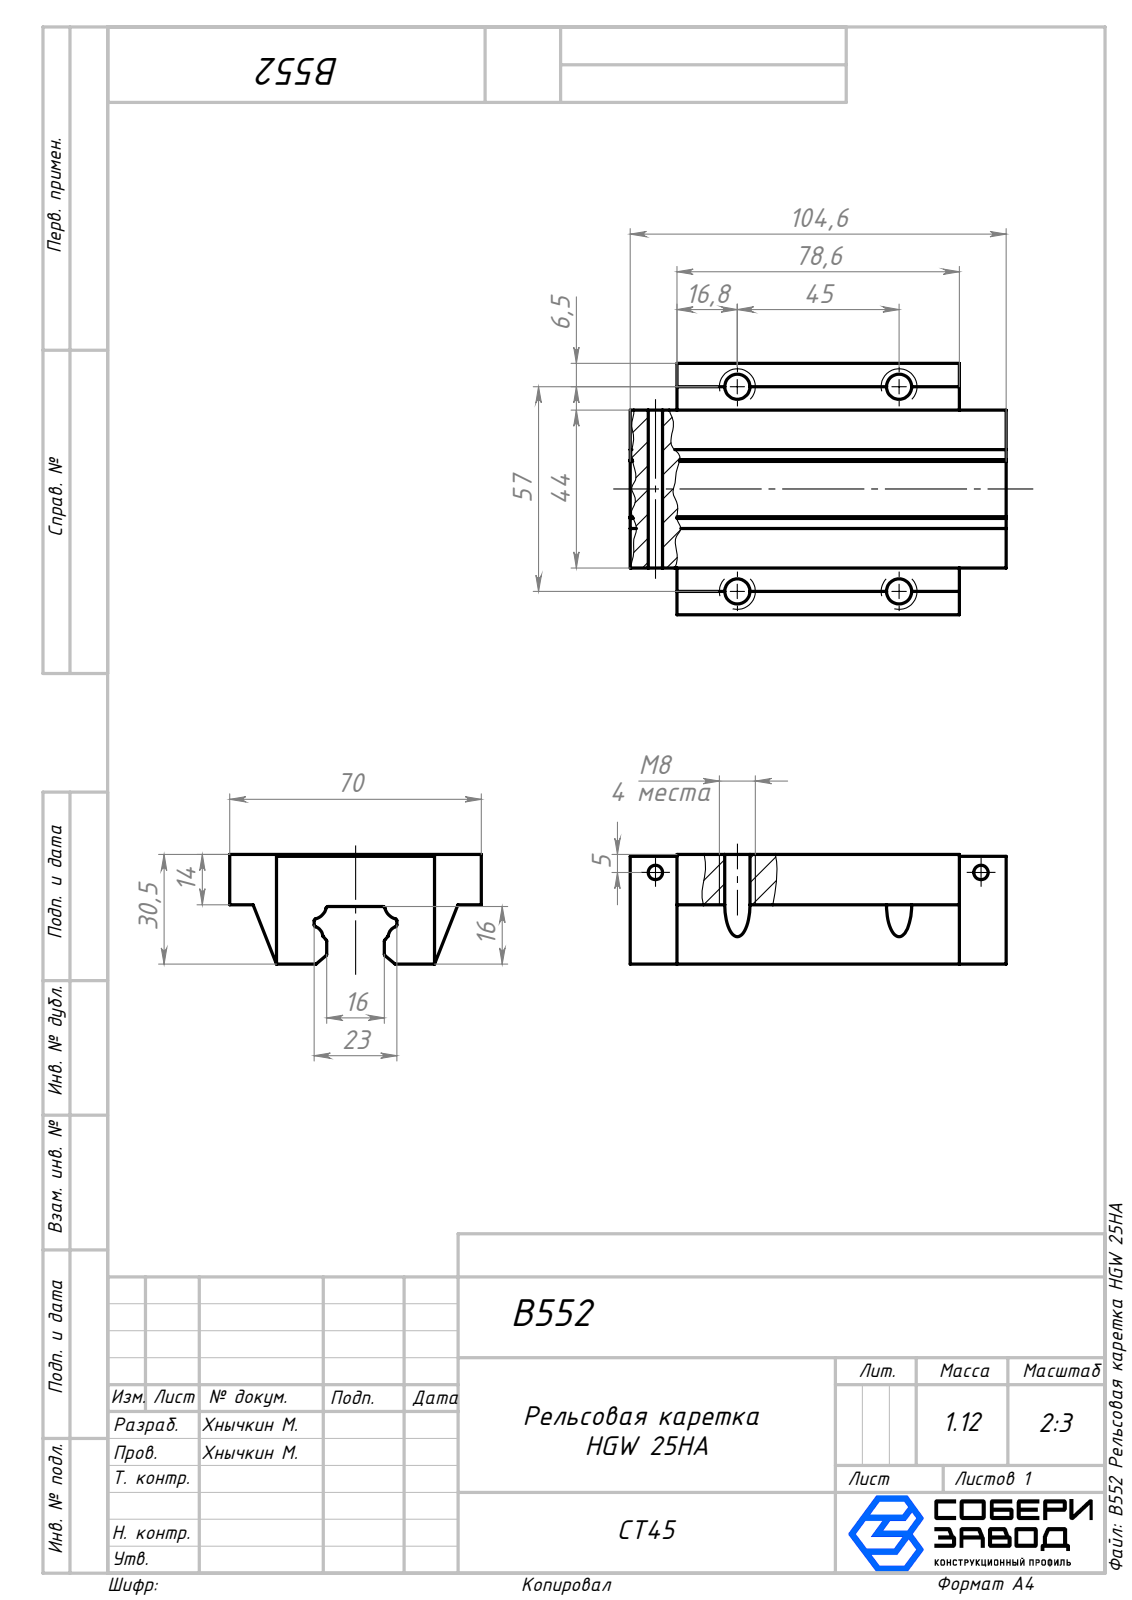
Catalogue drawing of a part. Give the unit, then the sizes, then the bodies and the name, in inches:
Units: inches
Overall size (bounding box): 4.118 × 2.756 × 1.201
Round holes (diameter × count): ⌀0.276 ×4, ⌀0.157 ×2
Partial cylindrical surfaces — rounded edges, fillets, slot ends (radius × count): R0.02 ×12, R0.118 ×2, R0.157 ×2
Main face-to-face distances: 0.551, 0.512, 1.201, 0.02, 0.63, 1.181, 0.571, 2.244, 2.756, 4.118
Hole centre spacings: 1.772, 2.244, 2.859, 3.567
Volume: 8.689 in³ · Surface area: 42.76 in²
Bodies: 1 solid, 56 faces (28 planar, 28 cylindrical, 0 other)
Part name (STEP PRODUCT): B552 Рельсовая каретка HGW 25HA
STEP written by: SolidWorks 2026 (AUTOMOTIVE_DESIGN)
